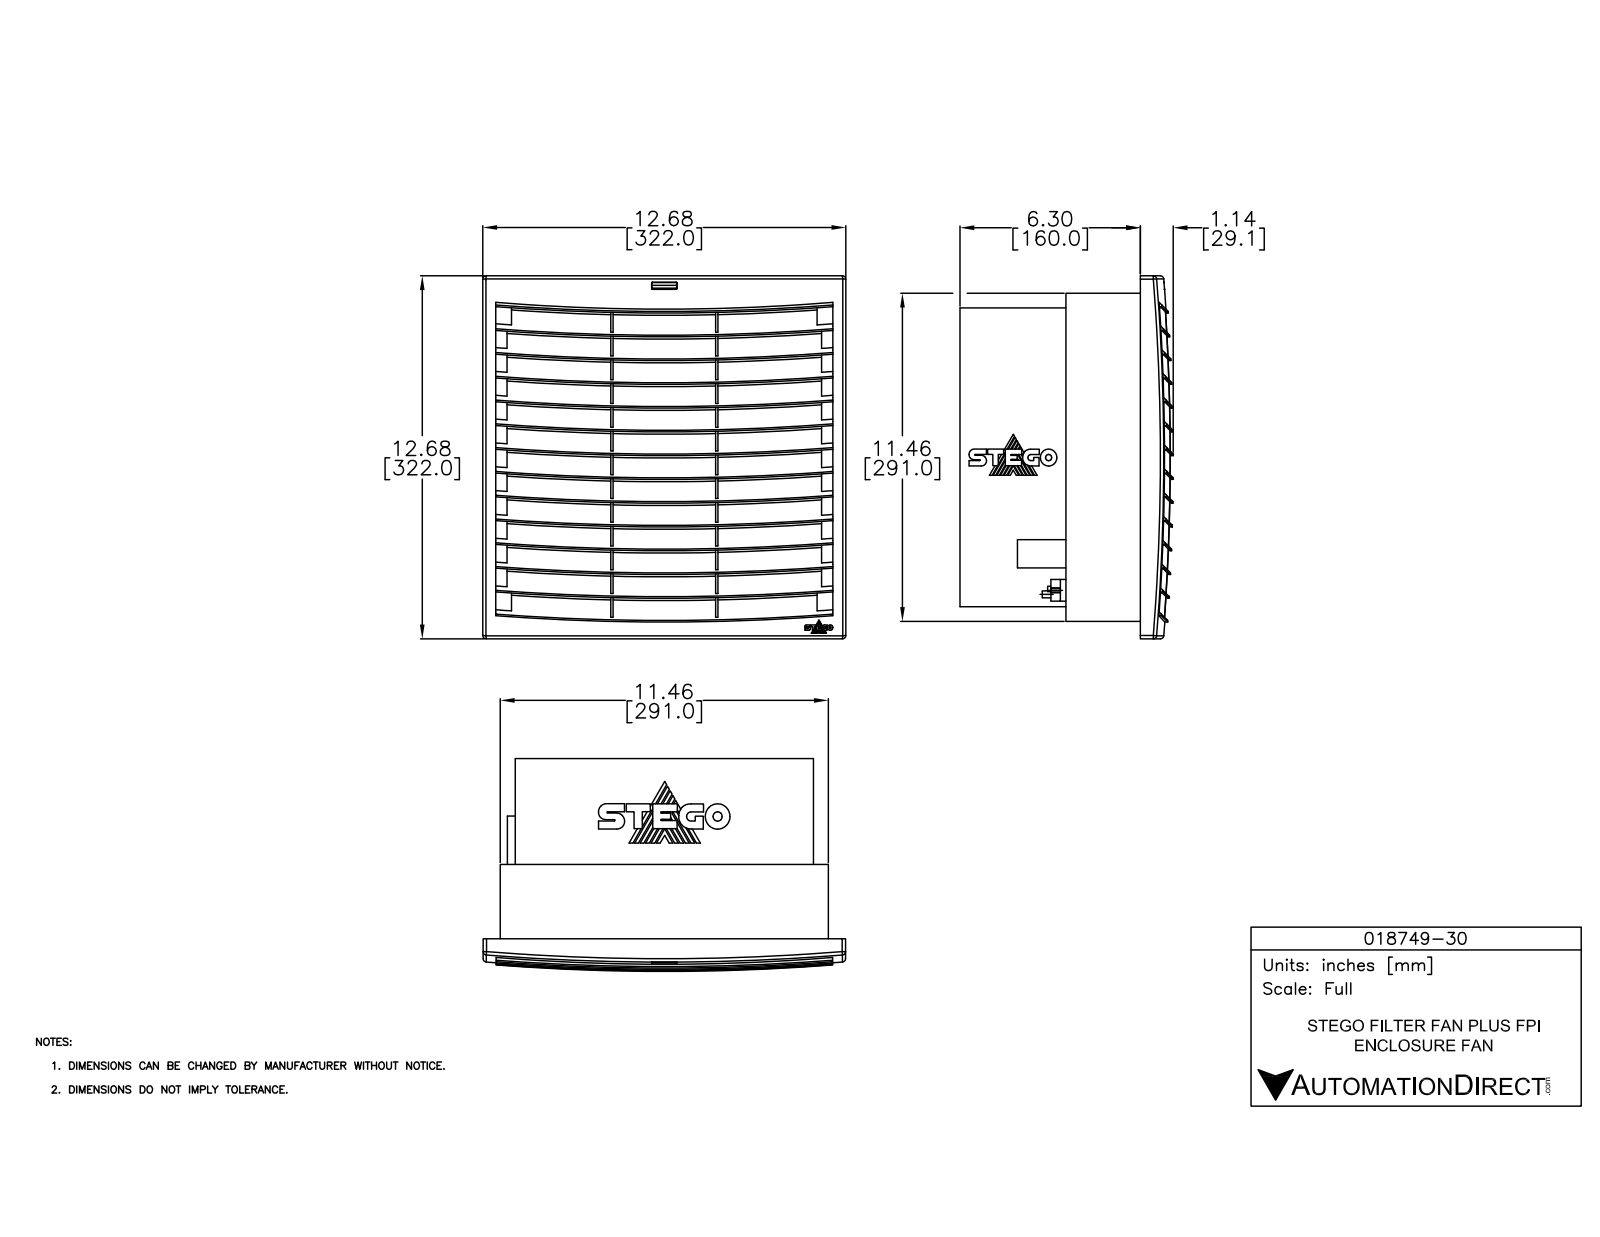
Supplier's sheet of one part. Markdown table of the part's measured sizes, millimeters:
| quantity | value |
| --- | --- |
| part name | 018749-30 |
| STEP written by | SolidWorks 2018 (AUTOMOTIVE_DESIGN) |
| units | millimeters |
| bodies | 1 solid, 837 faces (483 planar, 354 cylindrical, 0 other) |
| overall size | 322 × 322 × 189 |
| volume | 5 681 000 mm³ |
| surface area | 1 030 000 mm² |
| round holes (diameter × count) | 76.2 × 1, 101.3 × 1, 119.2 × 1, 126.5 × 1, 150.1 × 1, 151.6 × 1, 176.7 × 1, 181 × 1, 201.9 × 1, 211.9 × 1, 232 × 1, 247.3 × 1 |
| round bosses / shafts (diameter × count) | 289.3 × 1, 275.5 × 1, 272.7 × 1, 220.9 × 1, 211.9 × 1, 190 × 1, 186.7 × 1, 161.6 × 1 |
| partial cylindrical surfaces (radius × count) | 1650 × 23, 112.5 × 7, 7 × 4, 8.7 × 4, 30.9 × 1, 44.1 × 1, 48.6 × 1, 1123.1 × 1 |
| main face-to-face distances | 16.2, 32.3, 48.5, 15, 64.6, 5, 80.8, 1.5, 7.3, 283.7 |
